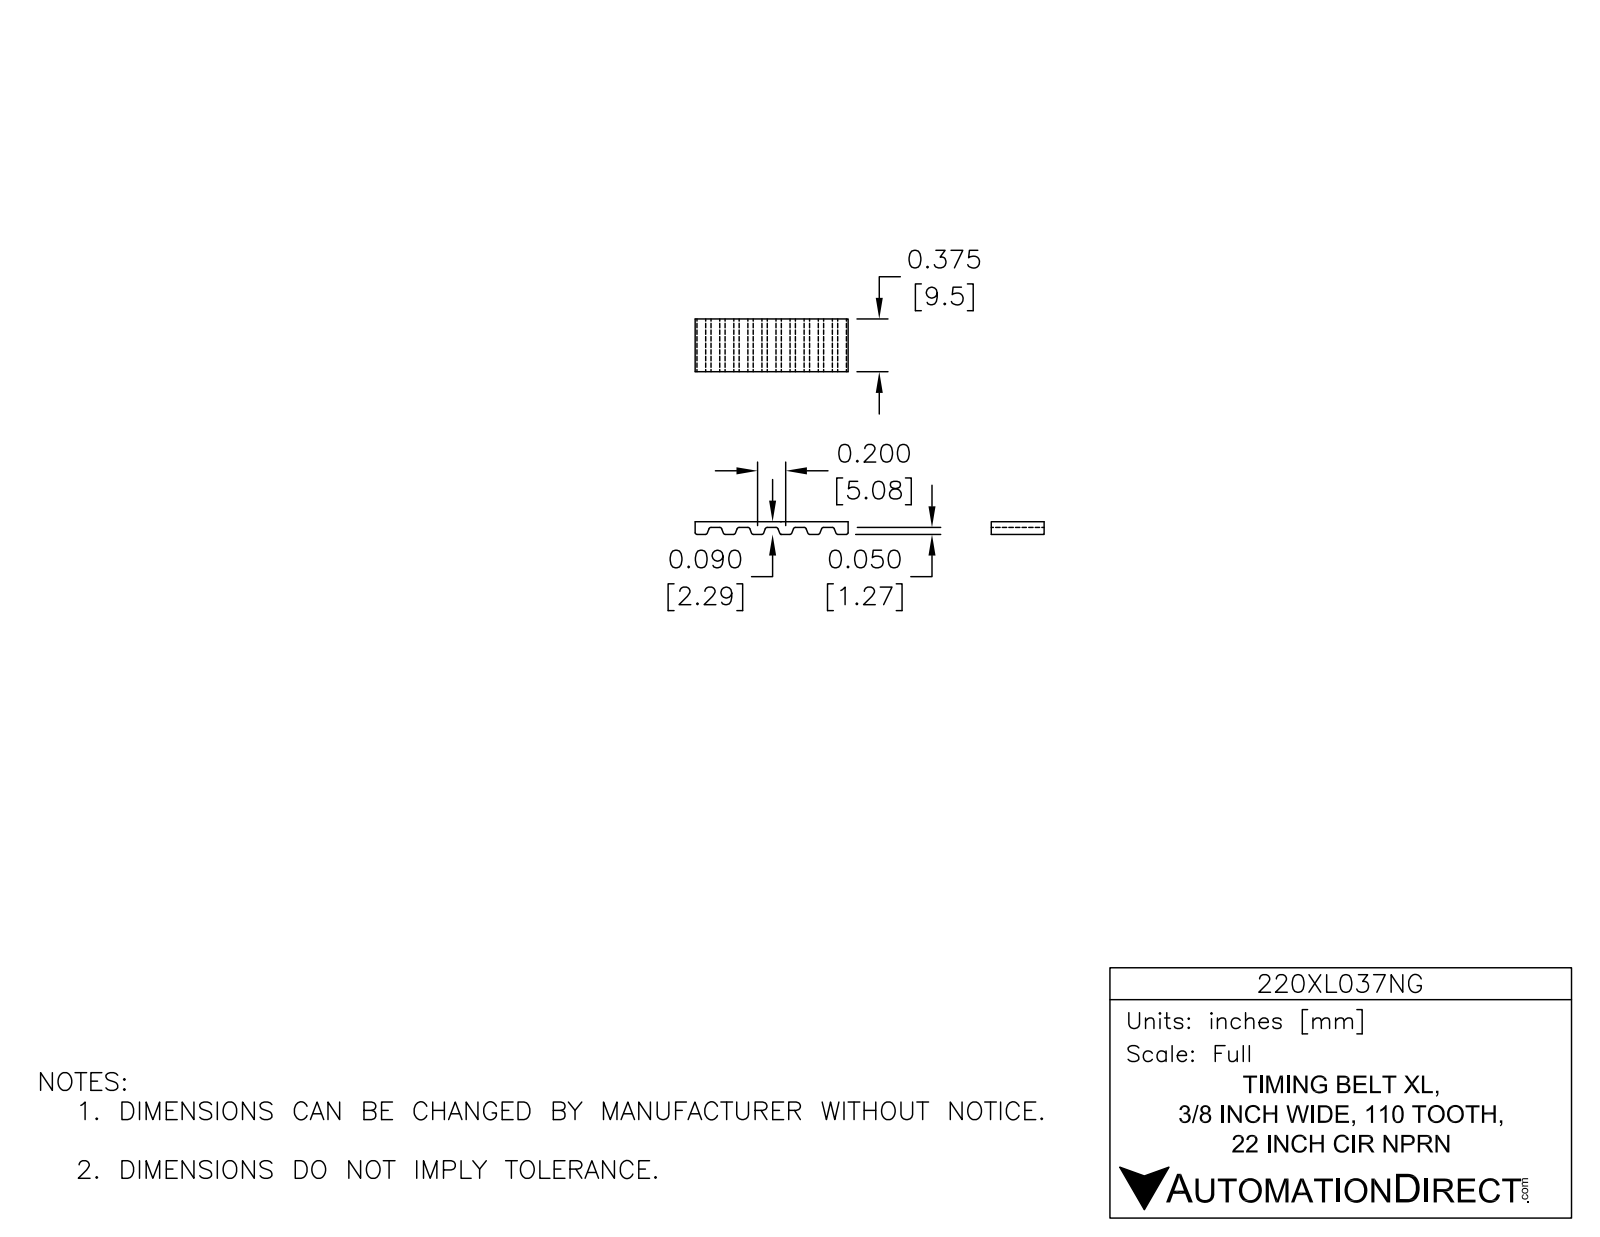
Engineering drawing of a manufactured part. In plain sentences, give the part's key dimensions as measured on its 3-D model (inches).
The part is named "220XL037NG". Its 3-D file was written by "SolidWorks 2014 (AUTOMOTIVE_DESIGN)". It is 1 solid with 918 faces: 398 planar, 520 cylindrical and 0 other. Overall it measures 9.288 by 3 by 0.375 inches. Its volume is 0.449 cubic inches and its surface area 21.08 square inches. Partial cylindrical surfaces (rounded edges, fillets, slot ends): 440 of radius 0.015, 2 of radius 1.46, 2 of radius 1.5. The main face-to-face distances are 3, 0.04, 2.96, 0.375, 2.92, 0.179, 0.358, 0.09, 2.91, 0.05.
